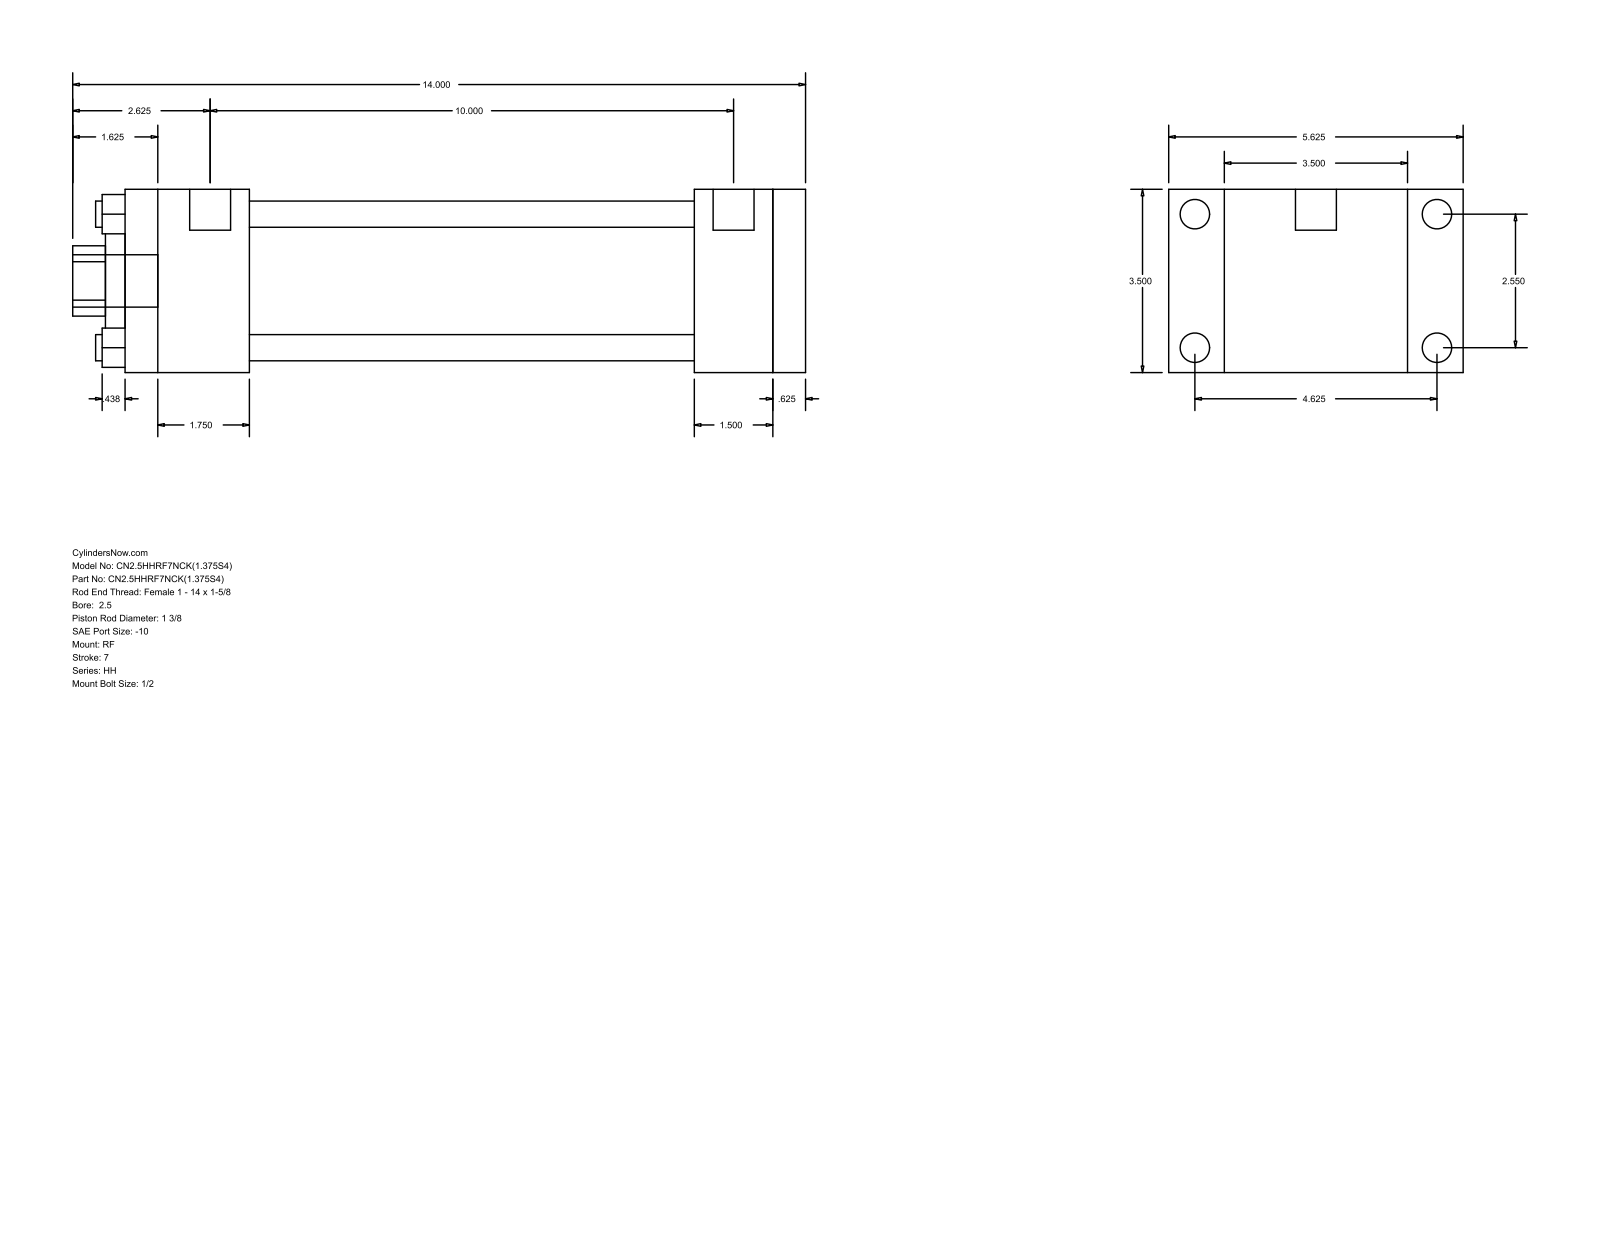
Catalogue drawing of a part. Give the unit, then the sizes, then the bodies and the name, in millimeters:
Units: millimetres
Overall size (bounding box): 355.6 × 142.88 × 88.9
Round holes (diameter × count): ⌀12.7 ×4, ⌀34.92 ×1, ⌀50.8 ×1, ⌀73.03 ×1
Round bosses / shafts (diameter × count): ⌀14.3 ×4, ⌀5.56 ×4, ⌀19.84 ×2, ⌀25.4 ×1
Partial cylindrical surfaces — rounded edges, fillets, slot ends (radius × count): R17.06 ×1
Main face-to-face distances: 88.9, 15.87, 314.33, 330.2, 60.32, 254.01, 269.88, 276.22, 215.9, 38.11
Hole centre spacings: 45.79, 64.76, 91.58
Bodies: 0 solids, 92 faces (64 planar, 28 cylindrical, 0 other)
Part name (STEP PRODUCT): HH_RF__0250_1.375
STEP written by: GSSL Pune (CONFIG_CONTROL_DESIGN)
